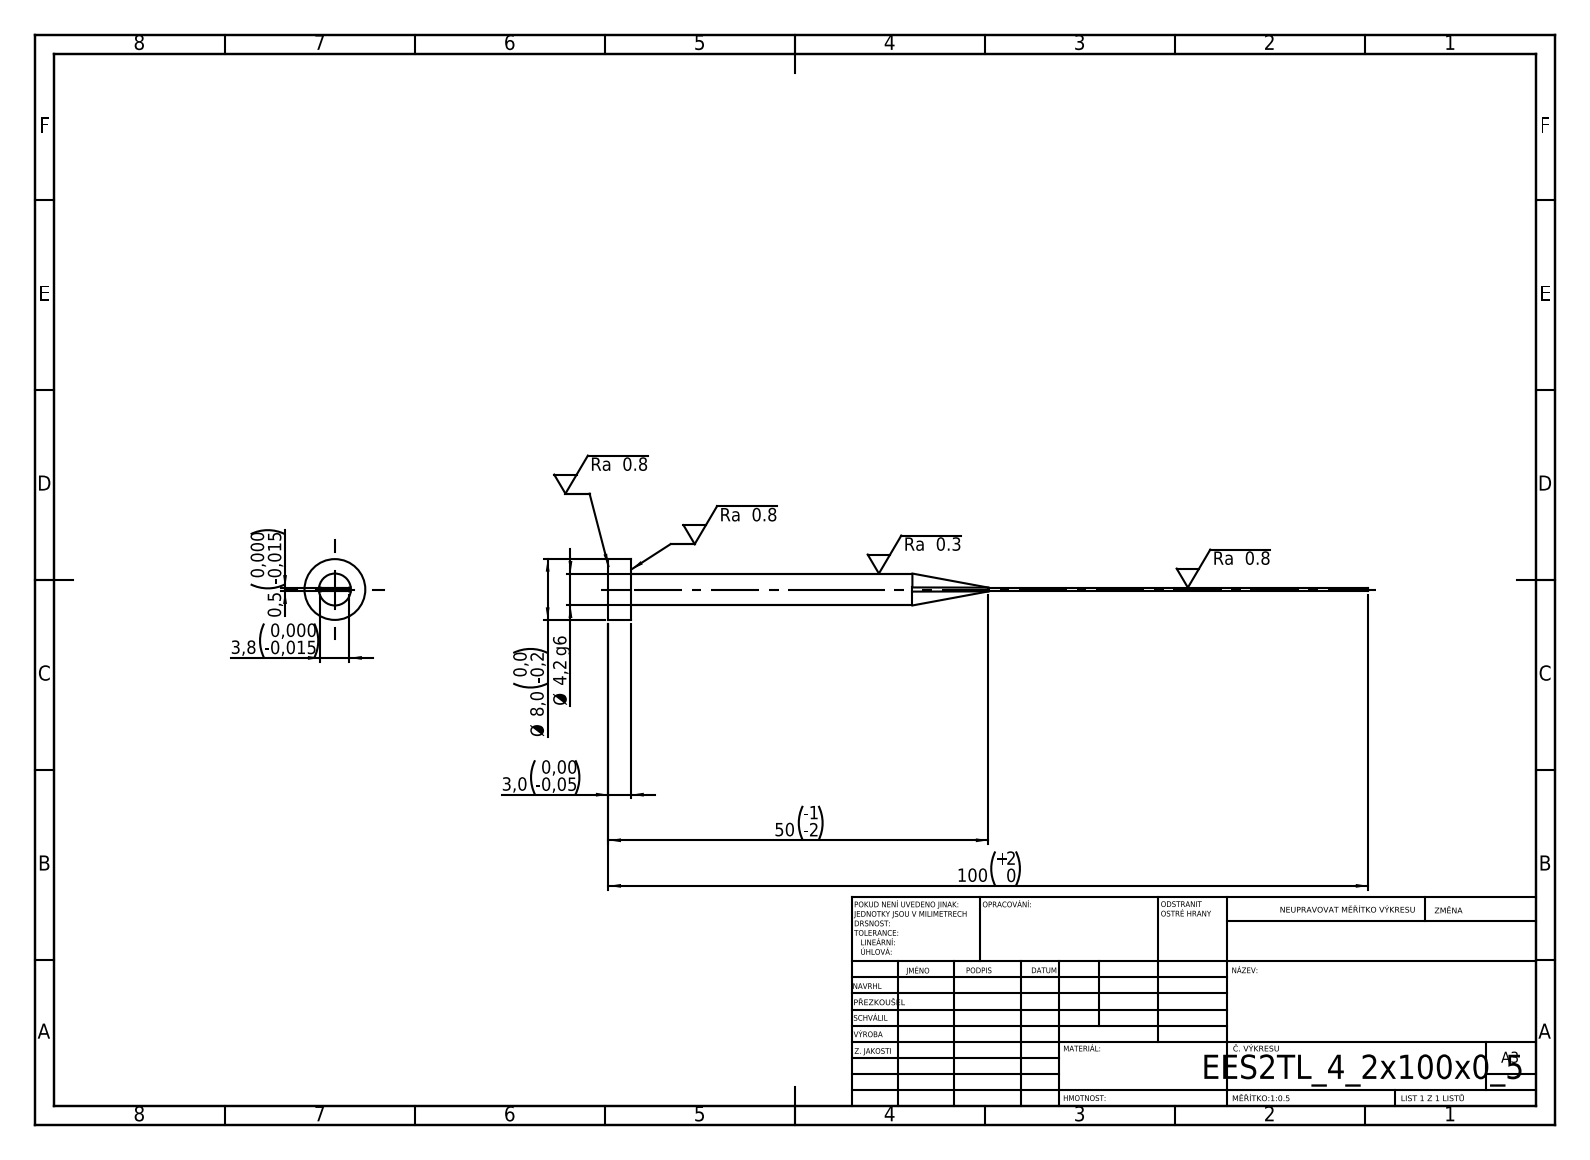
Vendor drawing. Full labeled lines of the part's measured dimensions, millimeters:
STEP written by: SolidWorks 2019 (CONFIG_CONTROL_DESIGN)
Units: millimetres
Bodies: 1 solid, 15 faces (7 planar, 4 cylindrical, 4 other)
Overall size (bounding box): 100 × 8 × 8
Volume: 831 mm³ · Surface area: 1 186 mm²
Round bosses / shafts (diameter × count): ⌀8 ×1, ⌀4.2 ×1
Main face-to-face distances: 0.5, 3, 3.8, 100, 97
